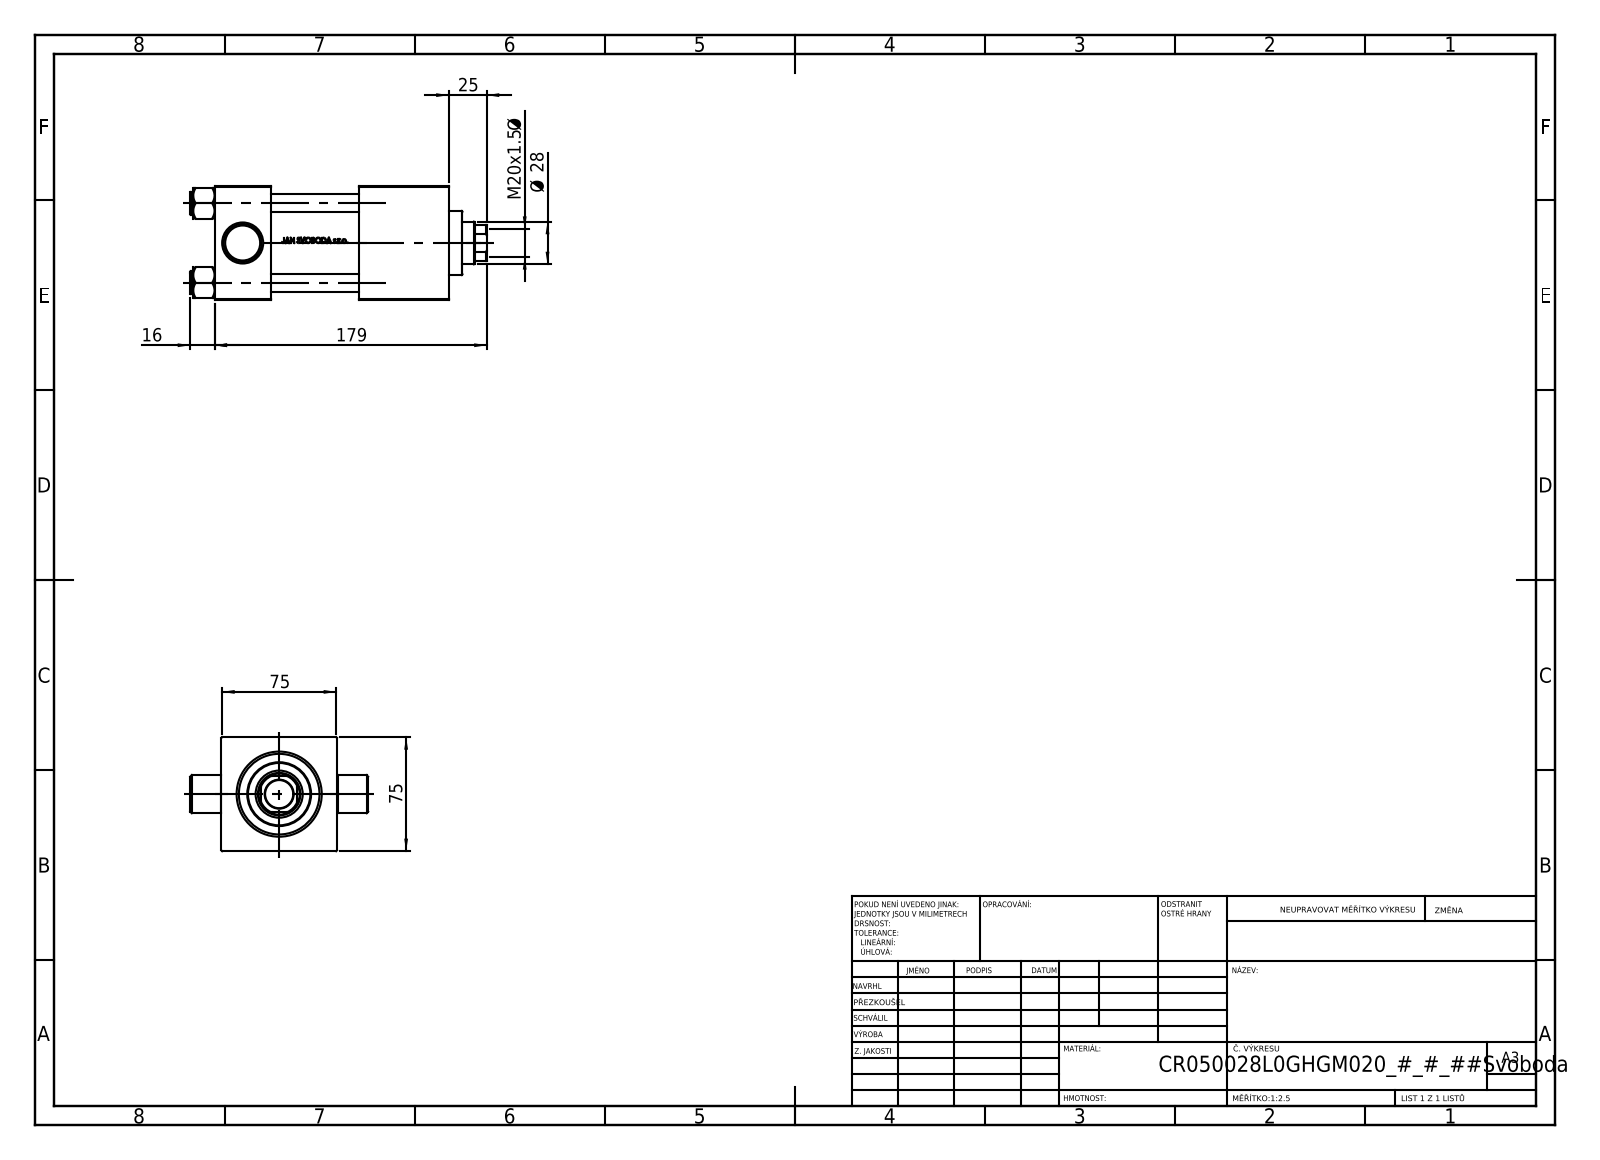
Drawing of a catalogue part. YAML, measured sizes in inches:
part_name: "V215_VC_A; V215CR_L_TYCINKA; V215CR_VCP_L; NUT_M5_L (+1 more)"
step_written_by: "SolidWorks 2019 (CONFIG_CONTROL_DESIGN)"
units: inches
bodies: {solids: 11, faces: 1057, planar: 425, cylindrical: 110, other: 522}
overall_size: [7.677, 4.606, 2.953]
volume: 43.53
surface_area: 228.7
round_holes:
  - {diameter: 0.472, count: 4}
  - {diameter: 0.276, count: 1}
  - {diameter: 0.728, count: 1}
  - {diameter: 1.102, count: 1}
  - {diameter: 1.22, count: 1}
  - {diameter: 1.614, count: 1}
  - {diameter: 1.969, count: 1}
  - {diameter: 2.087, count: 1}
round_bosses_or_shafts:
  - {diameter: 0.591, count: 4}
  - {diameter: 2.205, count: 1}
  - {diameter: 1.654, count: 1}
  - {diameter: 0.984, count: 1}
partial_cylinders:
  - {radius: 0.531, count: 1}
face_to_face_distances: [2.953, 1.457, 4.606, 0.02, 2.992, 2.972, 6.063, 2.283, 2.323, 3.74]
hole_center_spacings: [1.456, 2.059, 2.912]
